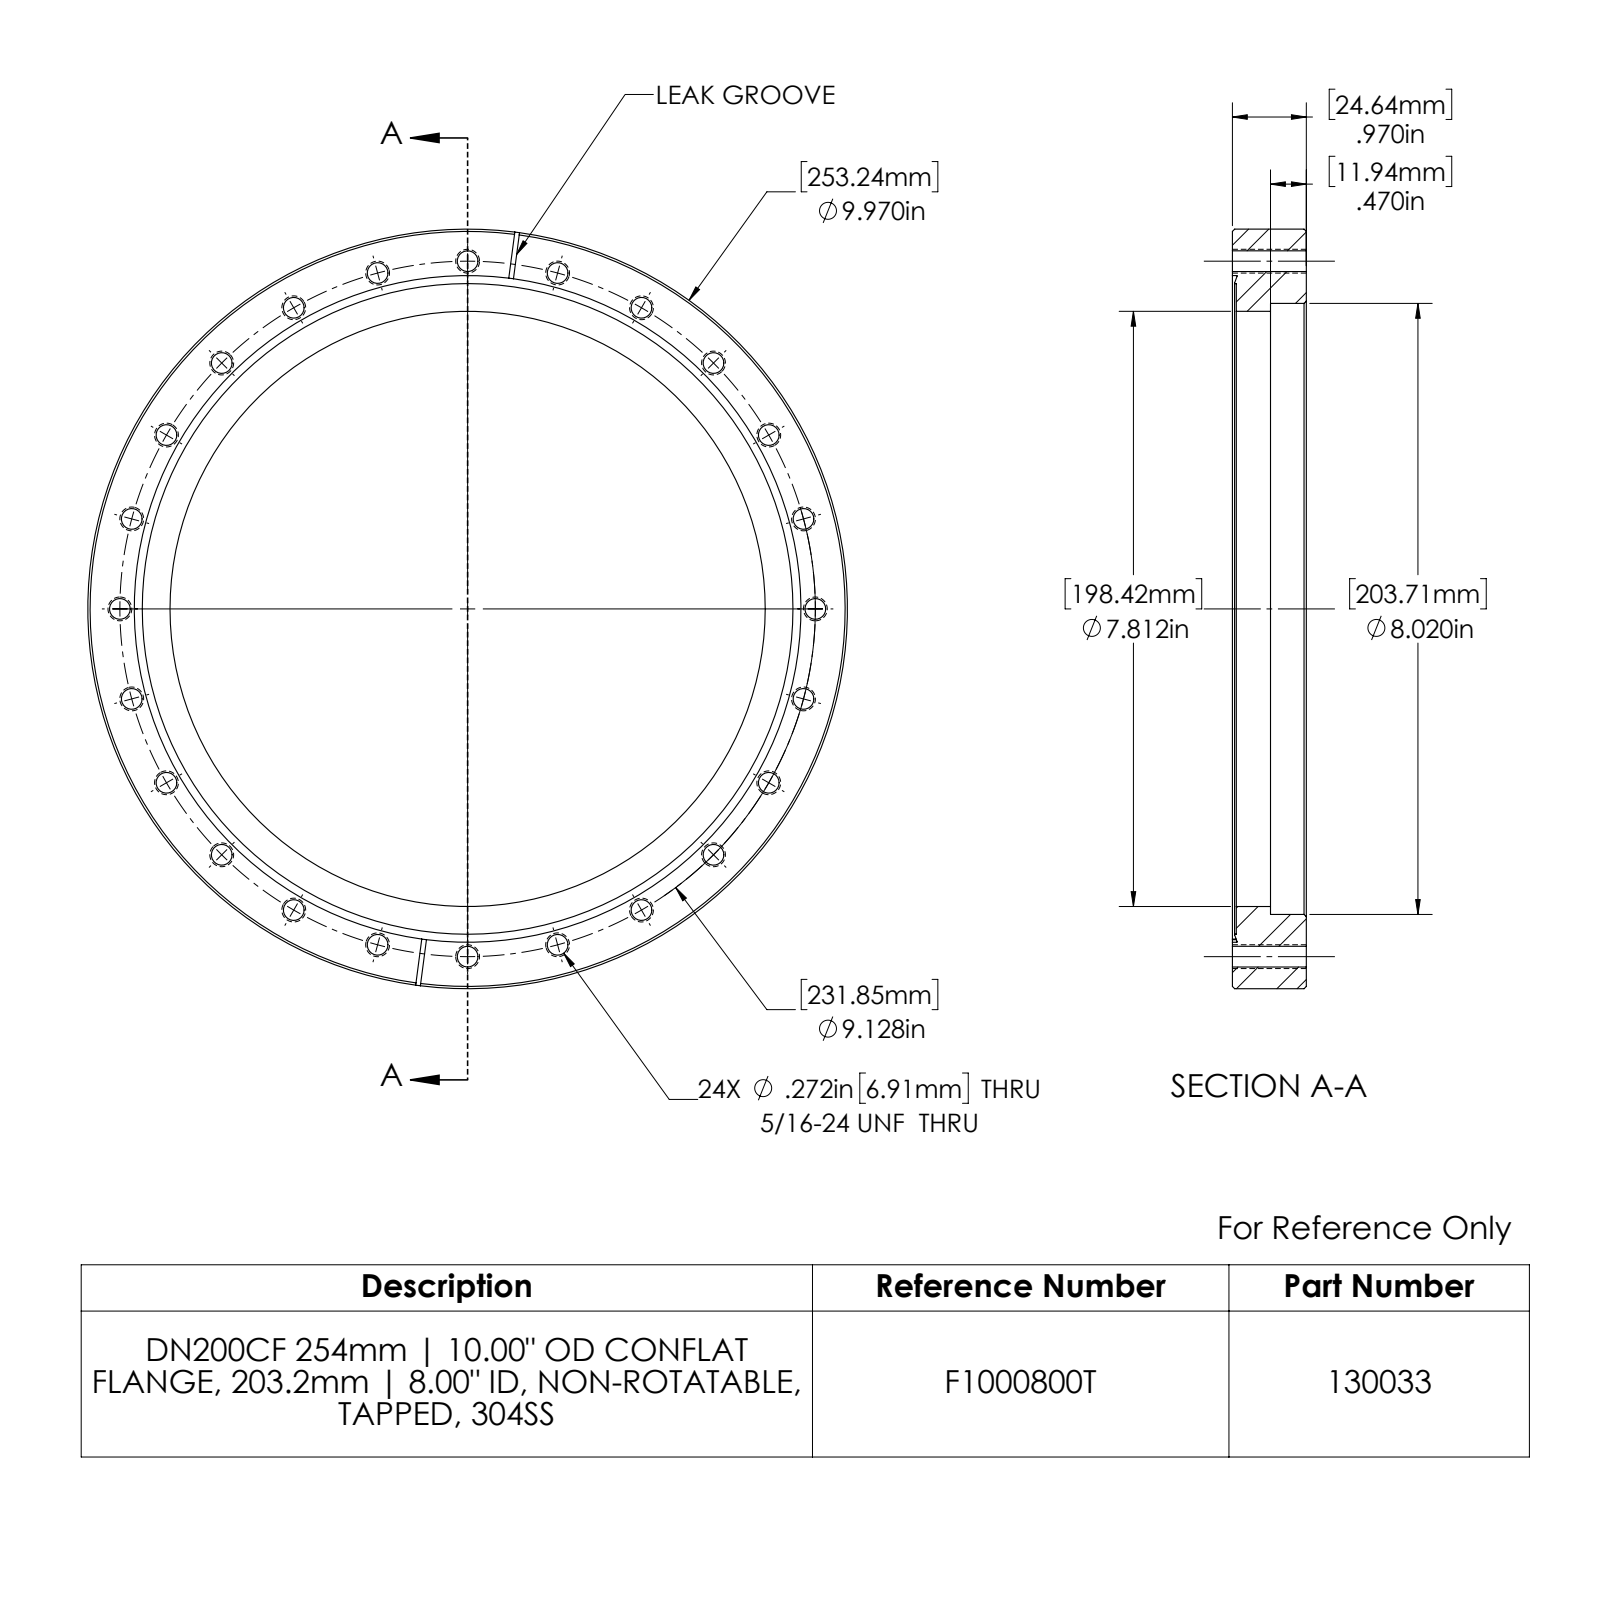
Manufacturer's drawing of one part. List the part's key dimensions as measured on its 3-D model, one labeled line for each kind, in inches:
Part name (STEP PRODUCT): 130033
STEP written by: SolidWorks 2022 (AUTOMOTIVE_DESIGN)
Units: inches
Bodies: 1 solid, 86 faces (9 planar, 60 cylindrical, 17 other)
Overall size (bounding box): 9.97 × 9.97 × 0.97
Volume: 26.01 in³ · Surface area: 131.6 in²
Round holes (diameter × count): ⌀0.272 ×24, ⌀7.812 ×1, ⌀8.02 ×1, ⌀8.54 ×1, ⌀8.75 ×1
Round bosses / shafts (diameter × count): ⌀9.97 ×1
Partial cylindrical surfaces — rounded edges, fillets, slot ends (radius × count): R1.25 ×2
Main face-to-face distances: 0.97, 0.051, 0.919, 0.5, 0.449, 0.47, 0.062, 0.067, 0.057
Hole centre spacings: 4.564, 8.433, 2.363, 4.564, 7.905, 1.191, 3.493, 5.557
